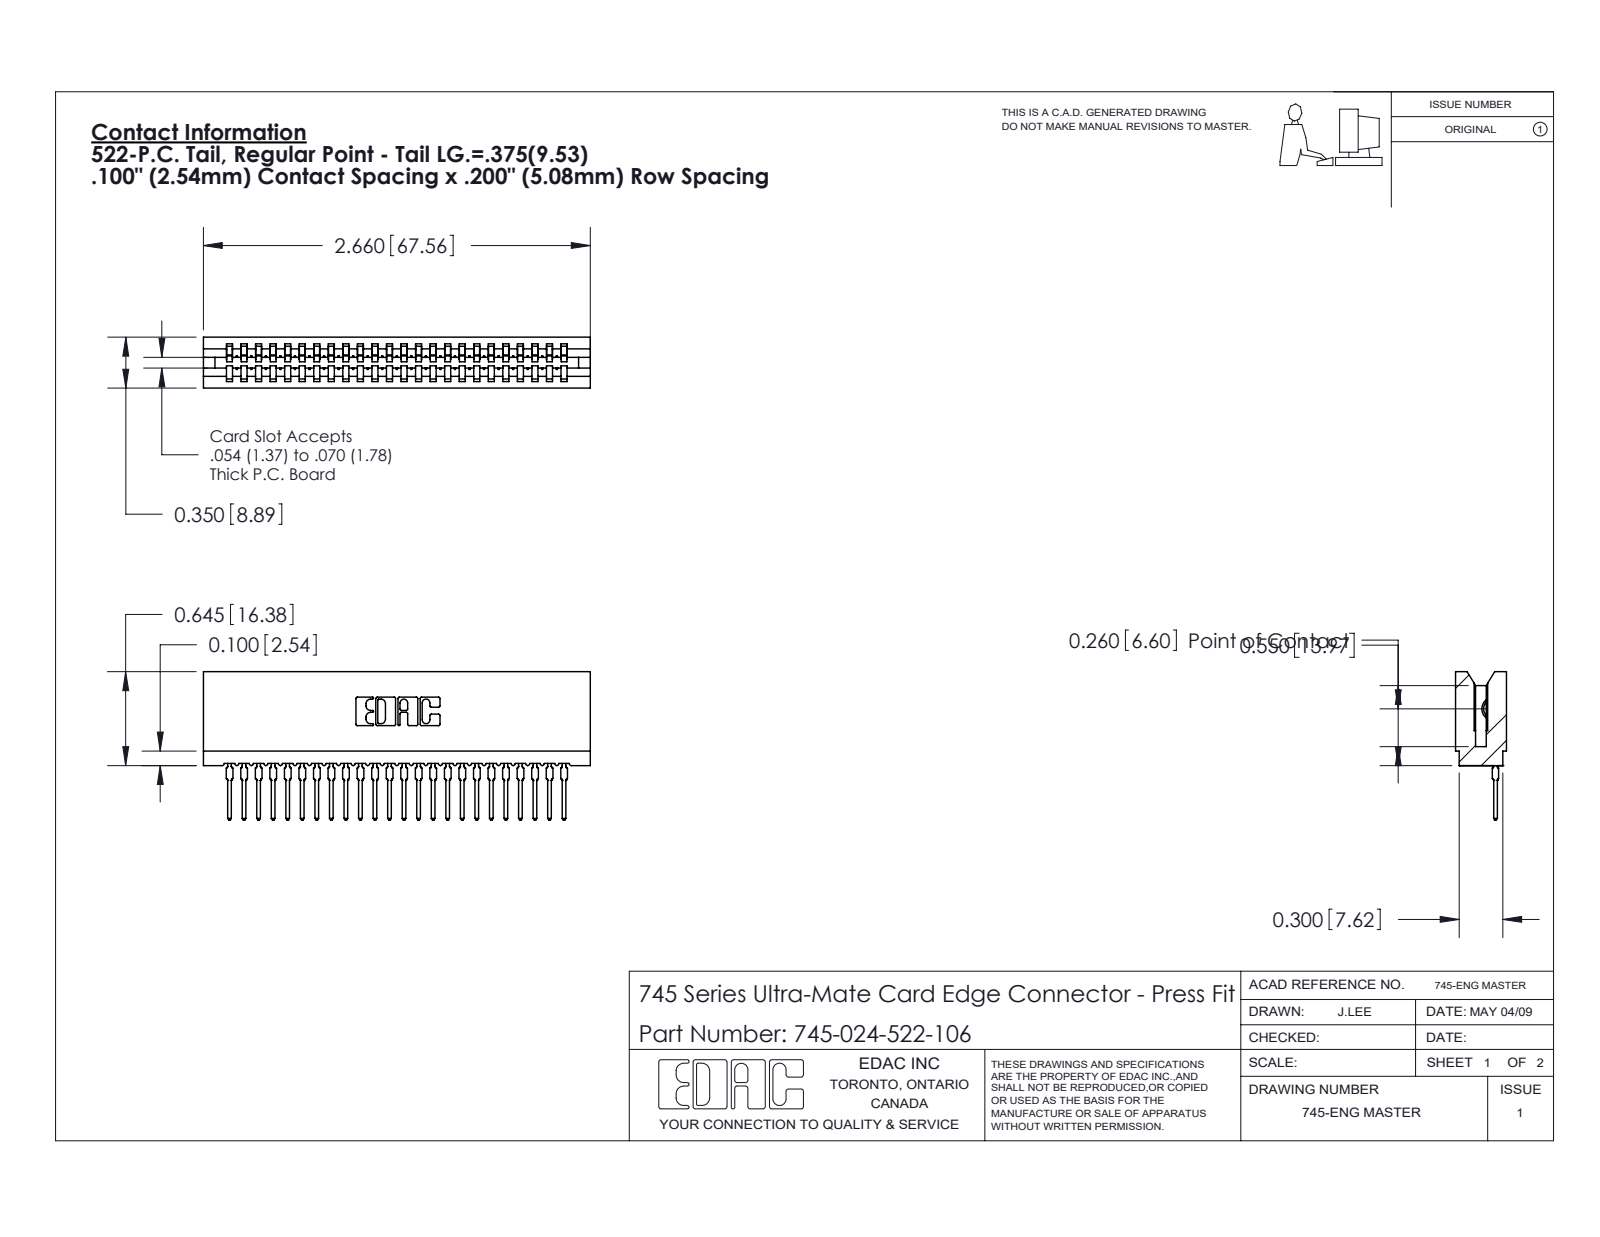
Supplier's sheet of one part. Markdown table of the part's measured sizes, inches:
| quantity | value |
| --- | --- |
| part name | 745 Part_Insulator Option - 06; 745-024-522-106; 745-292-001_522 |
| STEP written by | SolidWorks 2020 (CONFIG_CONTROL_DESIGN) |
| units | inches |
| bodies | 25 solids, 2784 faces (1664 planar, 496 cylindrical, 624 other) |
| overall size | 2.66 × 1.021 × 0.35 |
| volume | 0.364 in³ |
| surface area | 16.8 in² |
| partial cylindrical surfaces (radius × count) | 0.015 × 48, 0.021 × 48, 0.01 × 22, 0.007 × 6, 0.031 × 6, 0.005 × 4, 0.011 × 4, 0.026 × 3 |
| main face-to-face distances | 0.1, 0.35, 0.2, 0.138, 0.212, 0.3, 0.045, 0.305, 0.093, 0.167 |
